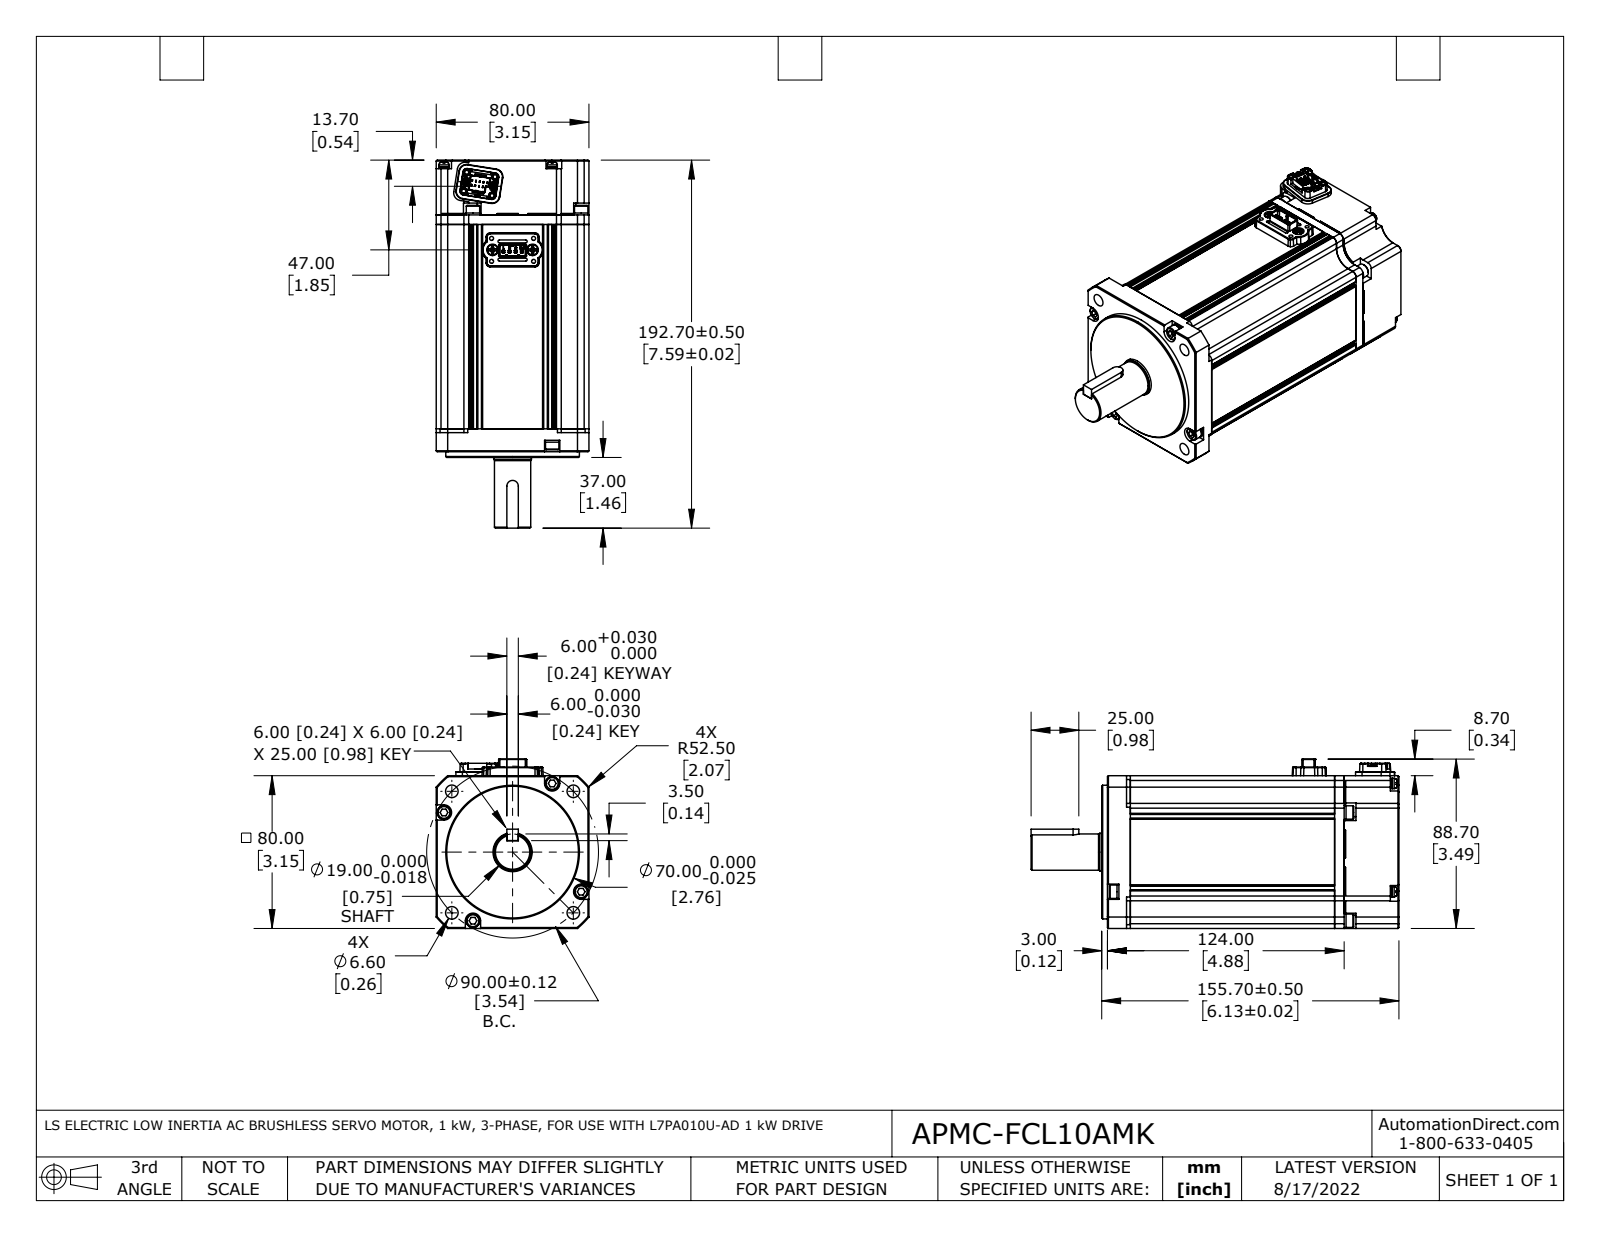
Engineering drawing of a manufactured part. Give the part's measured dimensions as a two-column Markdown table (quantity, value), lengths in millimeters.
| quantity | value |
| --- | --- |
| part name | SLM08GA001G04_Out Line(APMC-FCL10AMK) r1 nc fxt |
| STEP written by | SolidWorks 2017 (AUTOMOTIVE_DESIGN) |
| units | millimeters |
| bodies | 45 solids, 1859 faces (1195 planar, 483 cylindrical, 181 other) |
| overall size | 192.7 × 88.7 × 80 |
| volume | 882 100 mm³ |
| surface area | 124 300 mm² |
| round holes (diameter × count) | 2.1 × 10, 4 × 8, 4.5 × 8, 3 × 6, 3.5 × 4, 6.6 × 4, 2 × 2, 6 × 2, 3.3 × 1, 3.4 × 1, 20.5 × 1 |
| round bosses / shafts (diameter × count) | 7.2 × 8, 7 × 8, 5.4 × 6, 2.2 × 2, 70 × 1, 19.8 × 1, 19 × 1 |
| partial cylindrical surfaces (radius × count) | 0.3 × 36, 0.2 × 20, 0.2 × 9, 2.5 × 9, 1 × 8, 2 × 8, 0.5 × 7, 0.1 × 6 |
| main face-to-face distances | 80, 5, 107, 112, 0.7, 5.7, 112.7, 28, 28.7, 33.7 |
| hole center spacings | 41.5, 11.8, 52.7, 58.7, 68.7, 85.8, 6, 16 |
